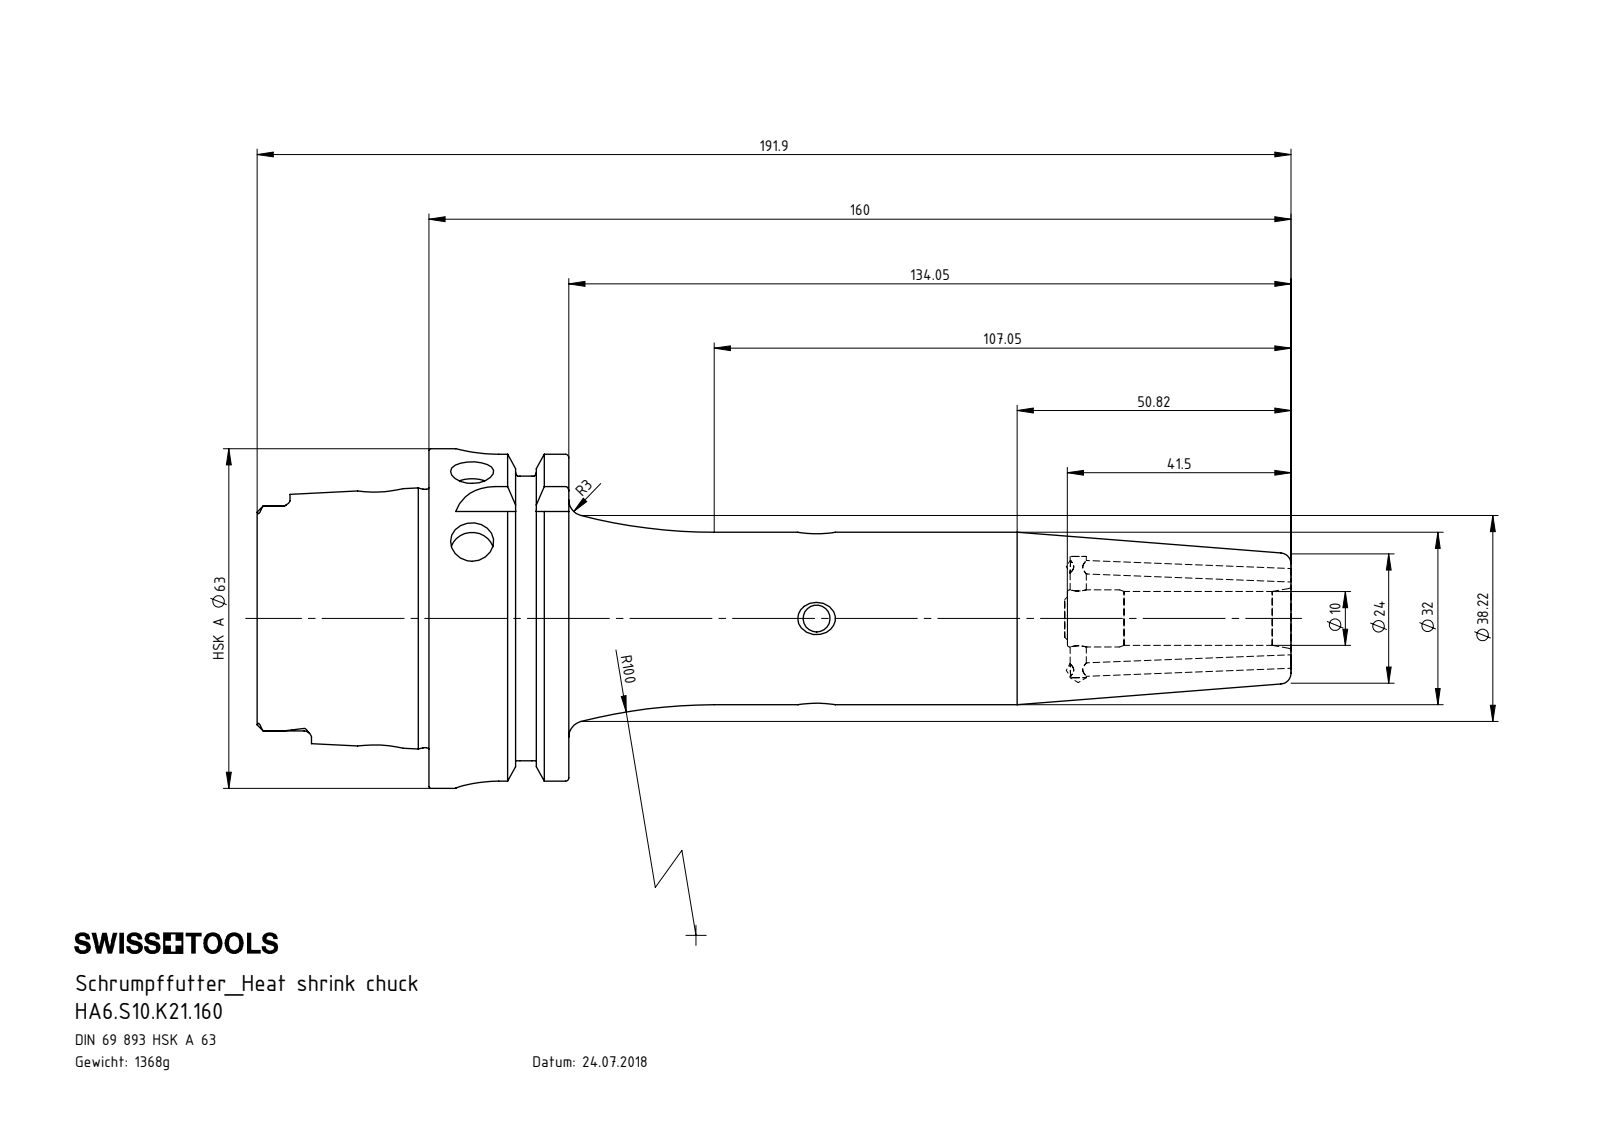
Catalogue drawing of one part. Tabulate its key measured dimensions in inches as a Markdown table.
| quantity | value |
| --- | --- |
| part name | HA6-S10.K21.160; ERU-AN3.K01.020_A; ERU-CJ2.001.006; HA6-S10.K21.160_C_Fertigbearbeitung |
| STEP written by | SolidWorks 2012 (CONFIG_CONTROL_DESIGN) |
| units | inches |
| bodies | 4 solids, 319 faces (101 planar, 87 cylindrical, 131 other) |
| overall size | 7.558 × 2.48 × 2.48 |
| volume | 10.63 in³ |
| surface area | 62.78 in² |
| round holes (diameter × count) | 0.098 × 2, 0.197 × 2, 0.315 × 2, 0.394 × 2, 0.118 × 1, 0.157 × 1, 0.276 × 1, 0.295 × 1, 0.331 × 1, 0.417 × 1, 0.669 × 1, 0.748 × 1 |
| round bosses / shafts (diameter × count) | 0.118 × 2, 2.48 × 1, 2.163 × 1, 1.887 × 1, 1.26 × 1, 0.315 × 1 |
| partial cylindrical surfaces (radius × count) | 0.055 × 6, 0.113 × 4, 0.315 × 4 |
| main face-to-face distances | 1.022, 0.63, 0.392, 1.256, 1.648, 2.278, 2.079, 0.858, 0.467, 2.114 |
| hole center spacings | 1.911, 2.557, 3.187, 5.098 |
